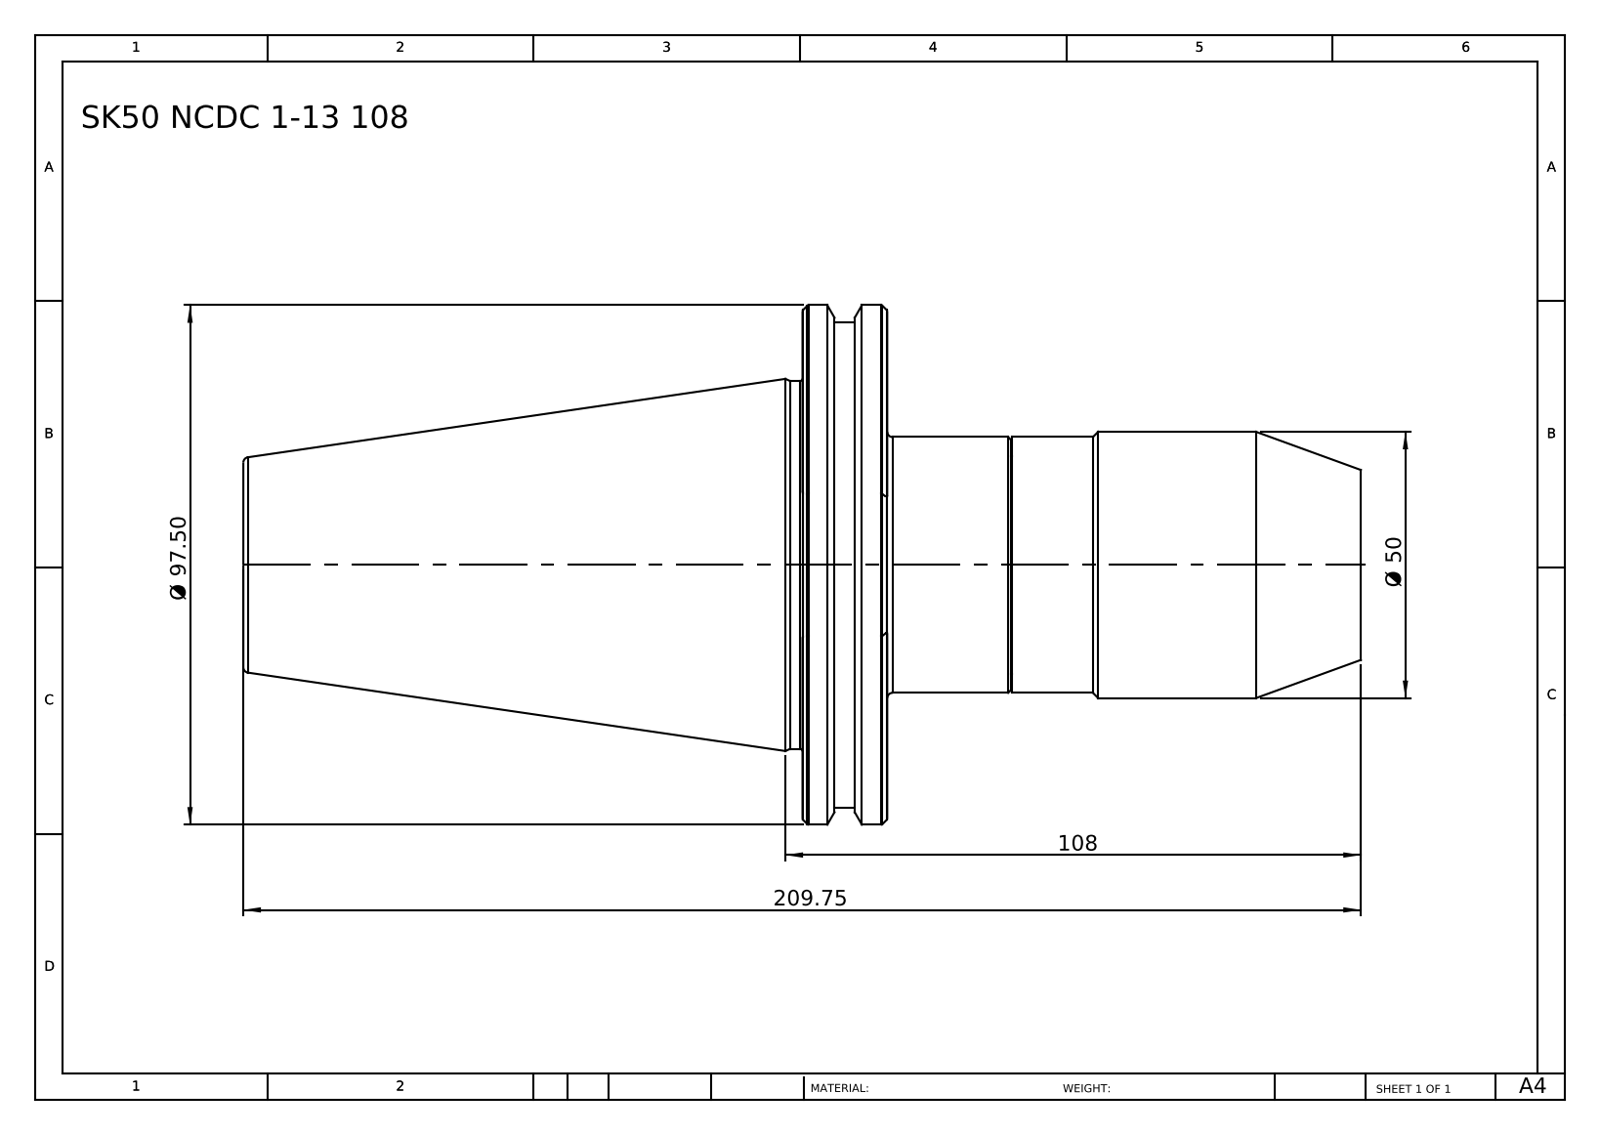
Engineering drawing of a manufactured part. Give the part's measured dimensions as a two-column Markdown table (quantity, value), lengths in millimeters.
| quantity | value |
| --- | --- |
| part name | SK50 NCDC 1-13 108 |
| STEP written by | SolidWorks 2014 (CONFIG_CONTROL_DESIGN) |
| units | millimeters |
| bodies | 1 solid, 81 faces (8 planar, 16 cylindrical, 57 other) |
| overall size | 209.75 × 97.5 × 97.5 |
| volume | 531 869 mm³ |
| surface area | 50 147 mm² |
| round bosses / shafts (diameter × count) | 97.5 × 1, 91 × 1, 69 × 1, 50 × 1, 48 × 1, 41 × 1 |
| main face-to-face distances | 15.9, 120.85, 104.95, 88.9, 104.8, 209.75, 65.4, 23.5, 39.4, 144.35 |
